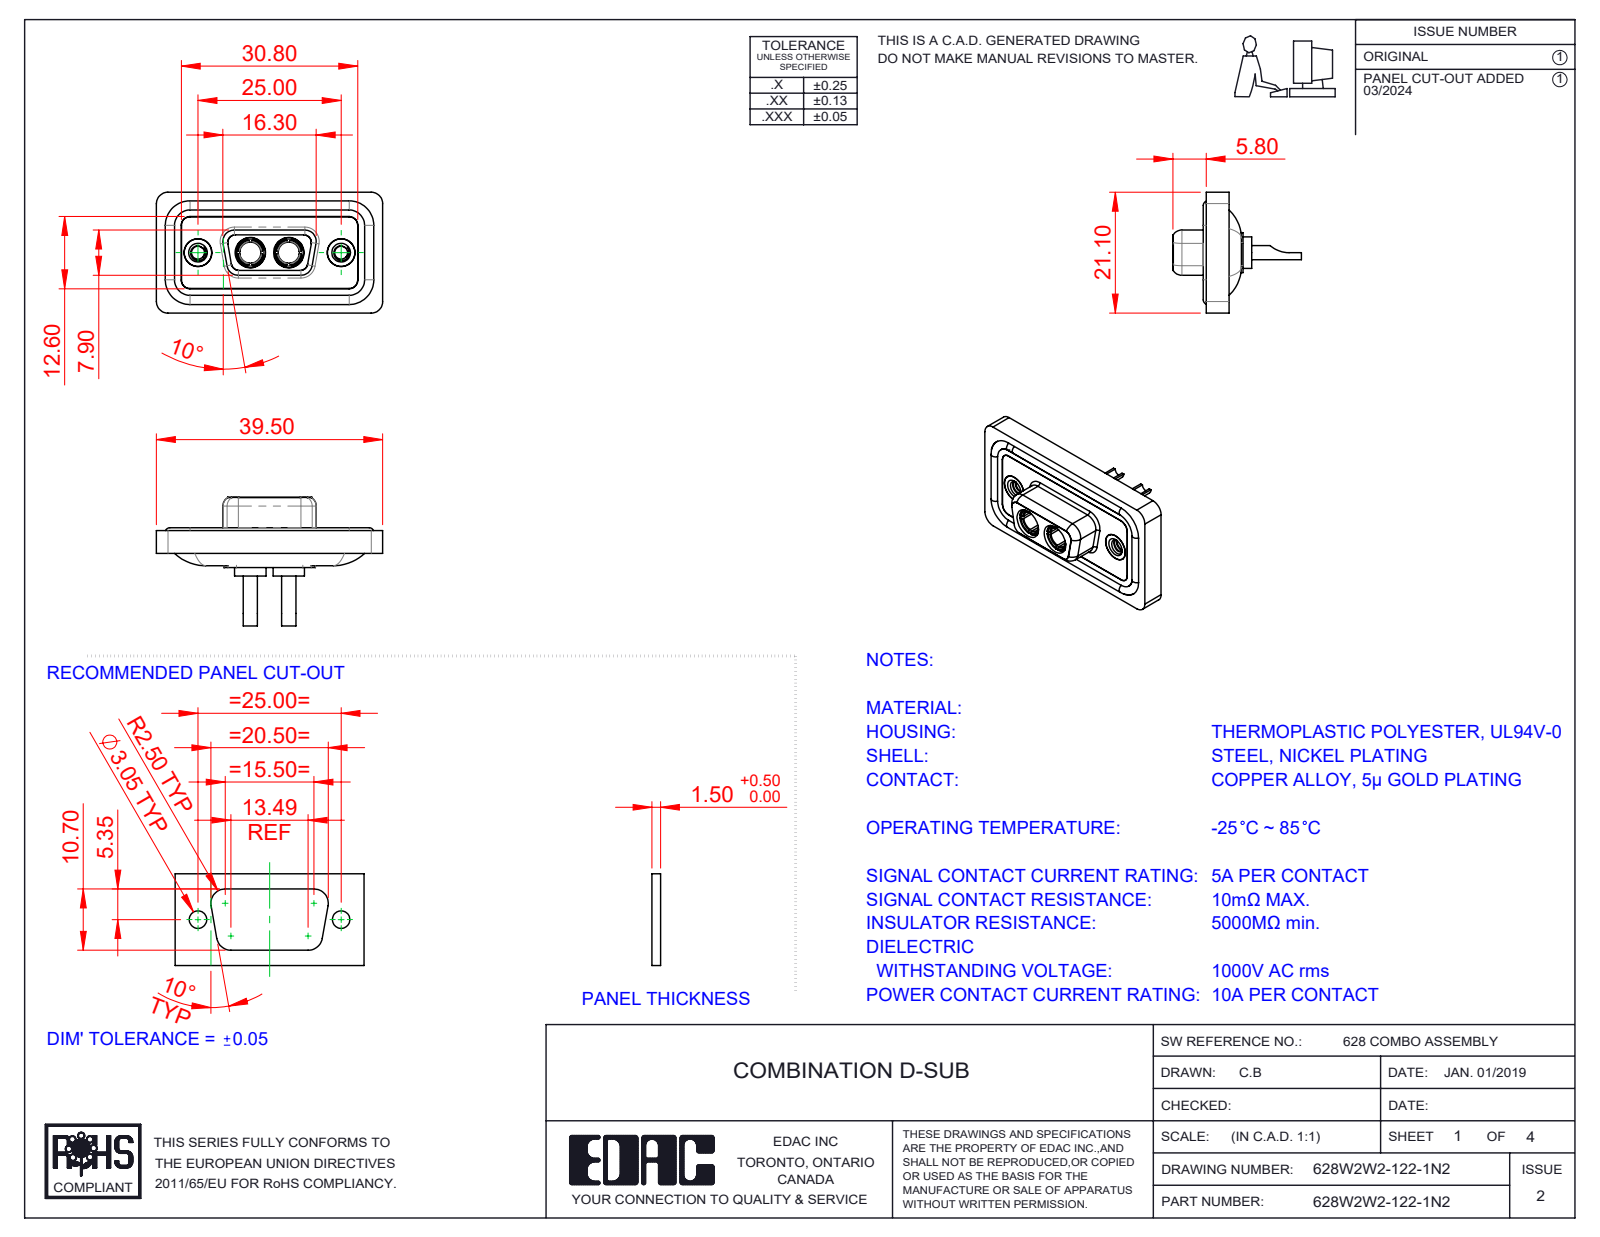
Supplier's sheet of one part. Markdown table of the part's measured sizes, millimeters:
| quantity | value |
| --- | --- |
| part name | 628Combo Waterproof Housing_09 Contacts; 628W2W2-122-1N2; 628Combo Shell Front_09 Contacts; 628Combo Housing_2W2 (+3 more) |
| STEP written by | SolidWorks 2023 (CONFIG_CONTROL_DESIGN) |
| units | millimeters |
| bodies | 11 solids, 544 faces (167 planar, 240 cylindrical, 137 other) |
| overall size | 39.5 × 22.45 × 21.1 |
| volume | 4 707 mm³ |
| surface area | 7 731 mm² |
| round holes (diameter × count) | 4.85 × 4, 1.7 × 2, 2.26 × 2, 3.7 × 2, 4 × 2, 4.05 × 2, 5 × 2, 5.3 × 2 |
| round bosses / shafts (diameter × count) | 1.6 × 4, 5.5 × 2, 5.2 × 2, 4.96 × 2, 4.95 × 2, 4.8 × 2, 4.75 × 2, 3.75 × 2 |
| partial cylindrical surfaces (radius × count) | 1.5 × 22, 2 × 18, 1.35 × 8, 1.6 × 8, 0.25 × 4, 0.5 × 4, 0.6 × 4, 0.65 × 4 |
| main face-to-face distances | 0.4, 1.8, 1.1, 2.9, 0.5, 1.6, 5.65, 7.45, 1.5, 5.35 |
| hole center spacings | 9.14, 15.86, 6.72, 25 |
